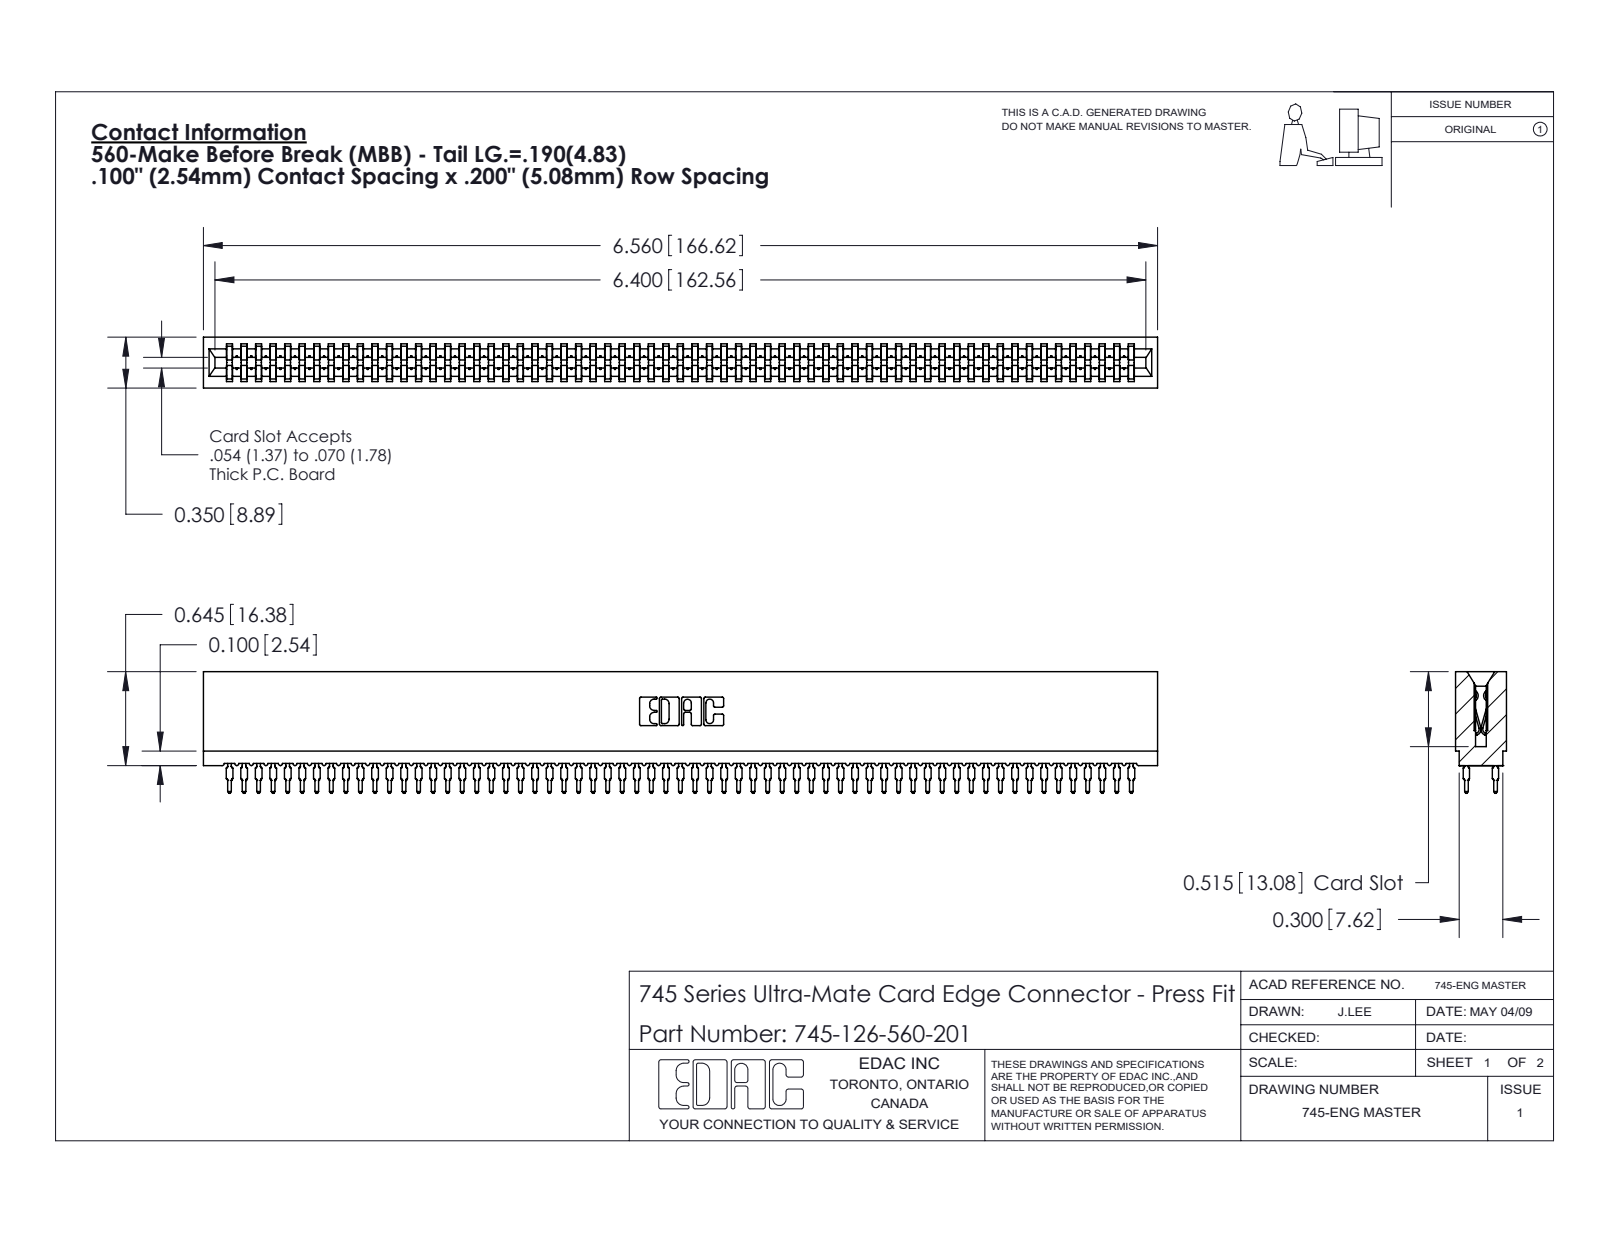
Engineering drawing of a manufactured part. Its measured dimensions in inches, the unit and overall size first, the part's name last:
Units: inches
Overall size (bounding box): 6.56 × 0.836 × 0.35
Partial cylindrical surfaces — rounded edges, fillets, slot ends (radius × count): R0.021 ×252, R0.015 ×126, R0.01 ×22, R0.005 ×8, R0.011 ×8, R0.007 ×6, R0.031 ×6, R0.026 ×3
Main face-to-face distances: 0.35, 0.063, 0.287, 0.045, 0.305, 0.018, 0.243, 0.138, 0.212, 0.093
Volume: 0.104 in³ · Surface area: 52.19 in²
Bodies: 126 solids, 12506 faces (6481 planar, 2749 cylindrical, 3276 other)
Part name (STEP PRODUCT): 745 Part_Insulator Option - 01; 745-292-001_560; 745-126-560-201
STEP written by: SolidWorks 2020 (CONFIG_CONTROL_DESIGN)
